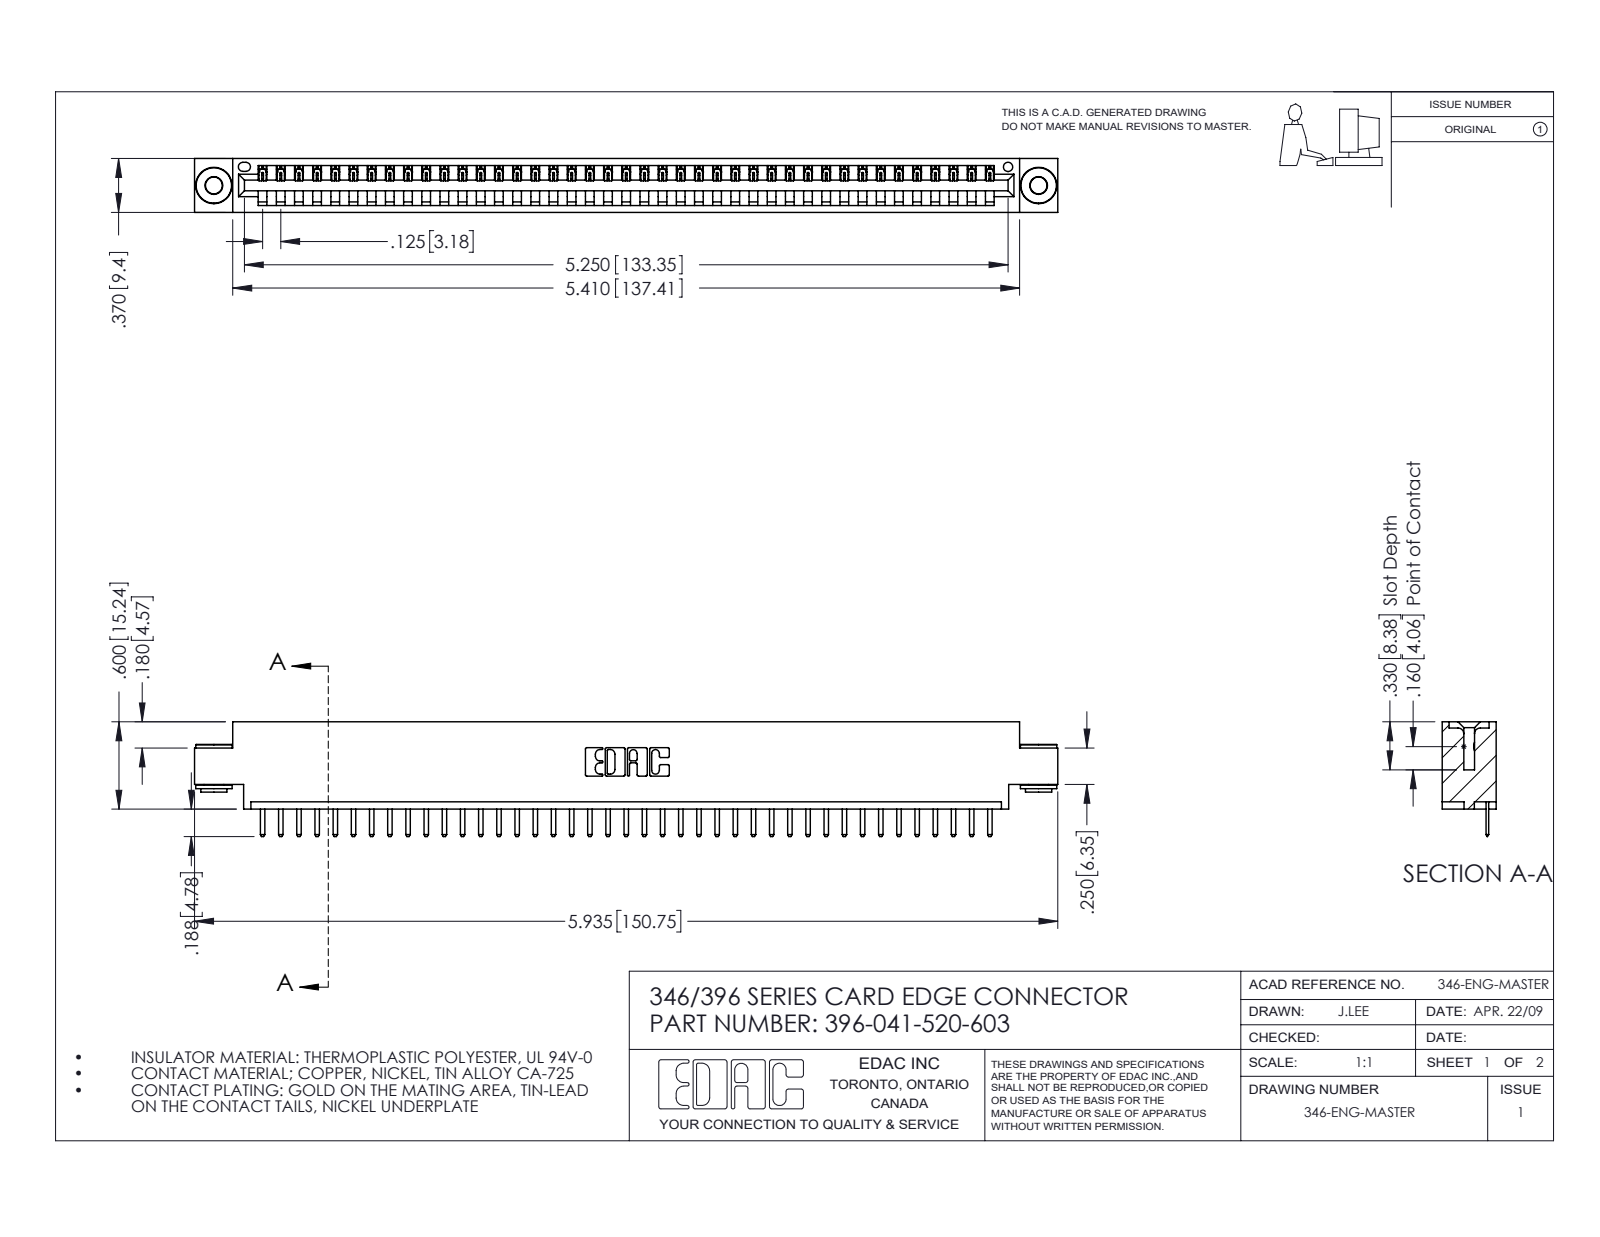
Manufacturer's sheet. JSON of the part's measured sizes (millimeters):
{"part_name": "345-292-001_345-293-120; 396-041-520-603; 346 Part_0.170 Offset - 0.156 Dia-TH; 345-250-002_345-250-002-102", "step_written_by": "SolidWorks 2016 (CONFIG_CONTROL_DESIGN)", "units": "millimeters", "bodies": {"solids": 44, "faces": 2706, "planar": 1812, "cylindrical": 886, "other": 8}, "overall_size": [150.7, 20, 9.4], "volume_mm3": 14200, "surface_area_mm2": 17680, "round_holes": [[2.9, 2], [4, 2], [1.6, 1]], "round_bosses_or_shafts": [[6.4, 2], [4.6, 2], [3.5, 2]], "partial_cylinders_radius": [[0.3, 84], [0.2, 82], [0.3, 22], [0.2, 6], [0.8, 6], [0.7, 3], [0.8, 2], [1, 2]], "face_to_face_distances": [1.2, 8.2, 9.4, 6.4, 0.6, 3.8, 5.6, 2.5, 4.4, 1.8], "hole_center_spacings": [6.2, 138.7, 144]}
